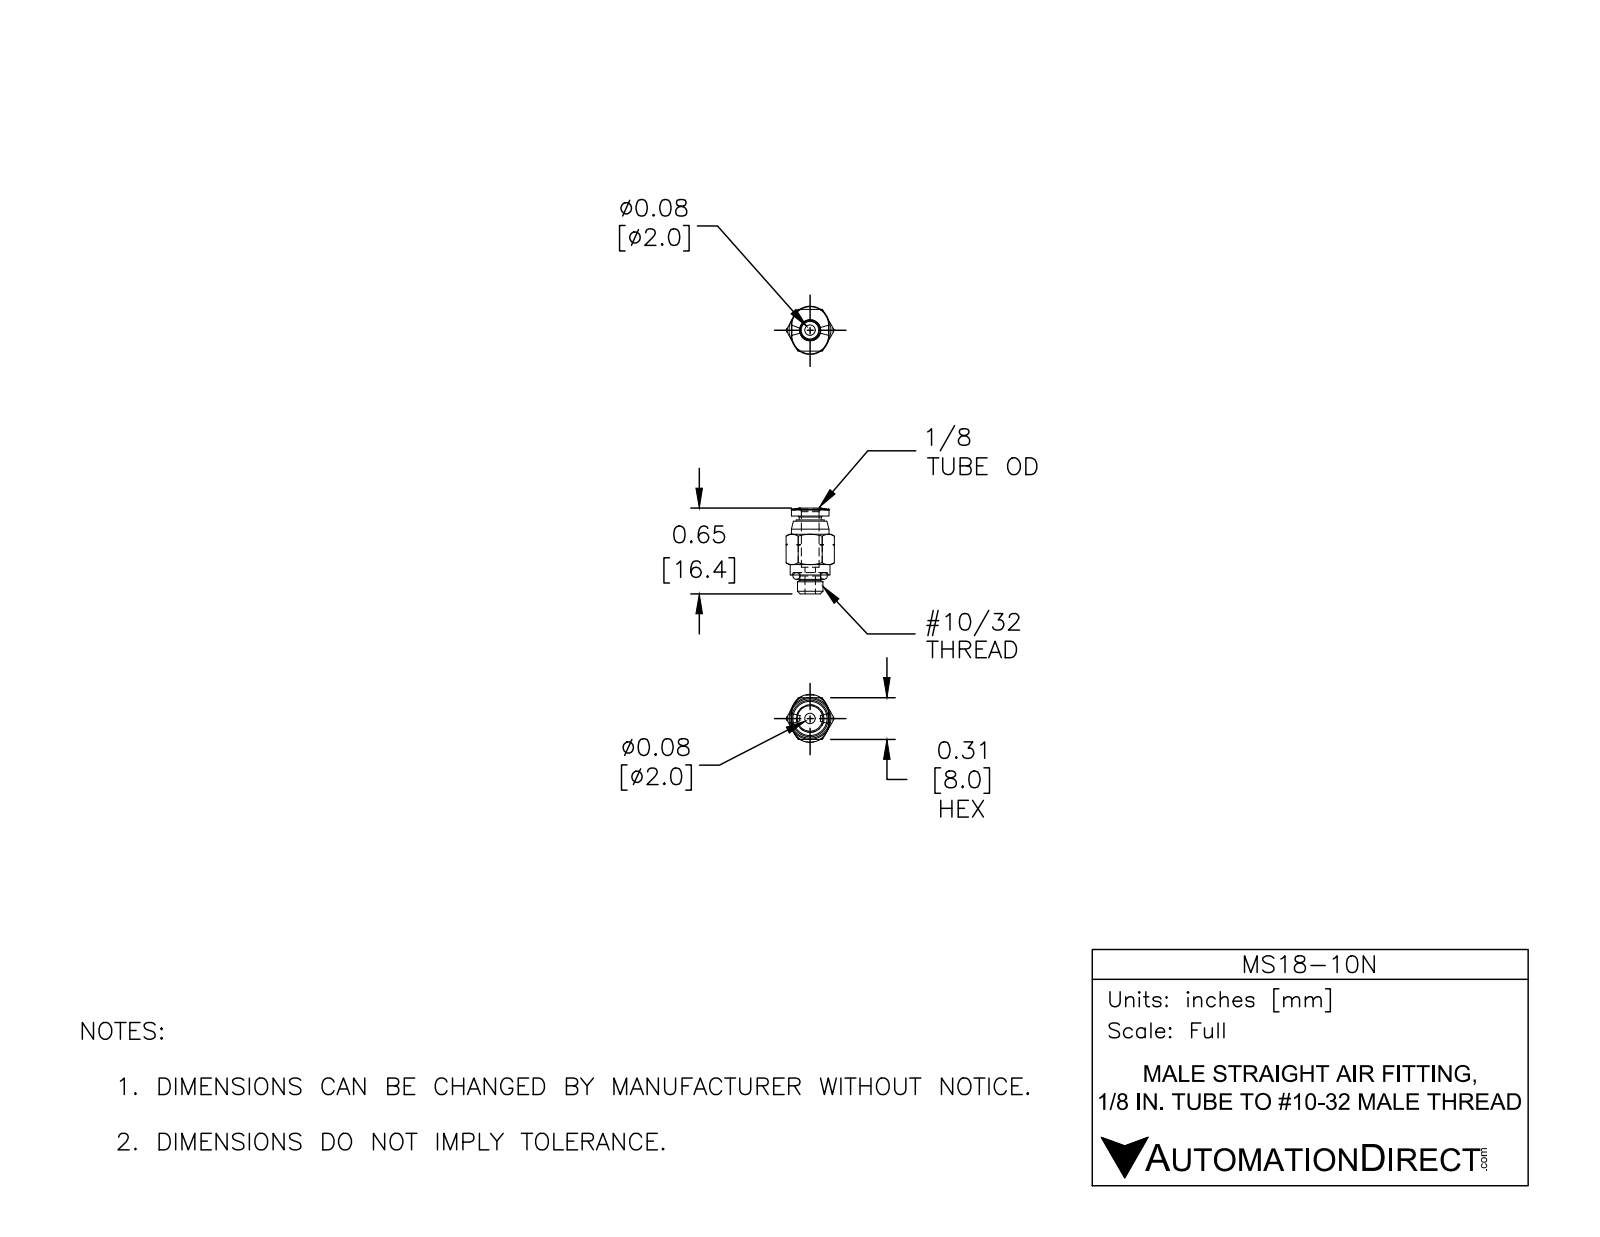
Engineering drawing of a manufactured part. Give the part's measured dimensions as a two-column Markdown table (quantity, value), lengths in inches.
| quantity | value |
| --- | --- |
| part name | MS18-10N |
| STEP written by | SolidWorks 2015 (CONFIG_CONTROL_DESIGN) |
| units | inches |
| bodies | 2 solids, 99 faces (19 planar, 20 cylindrical, 60 other) |
| overall size | 0.646 × 0.364 × 0.362 |
| volume | 0.033 in³ |
| surface area | 1.193 in² |
| round holes (diameter × count) | 0.079 × 1, 0.134 × 1 |
| round bosses / shafts (diameter × count) | 0.299 × 1, 0.283 × 1, 0.209 × 1, 0.19 × 1, 0.165 × 1, 0.156 × 1 |
| partial cylindrical surfaces (radius × count) | 0.142 × 2 |
| main face-to-face distances | 0.315, 0.425, 0.039, 0.386, 0.02, 0.059, 0.098, 0.287, 0.138, 0.161 |
